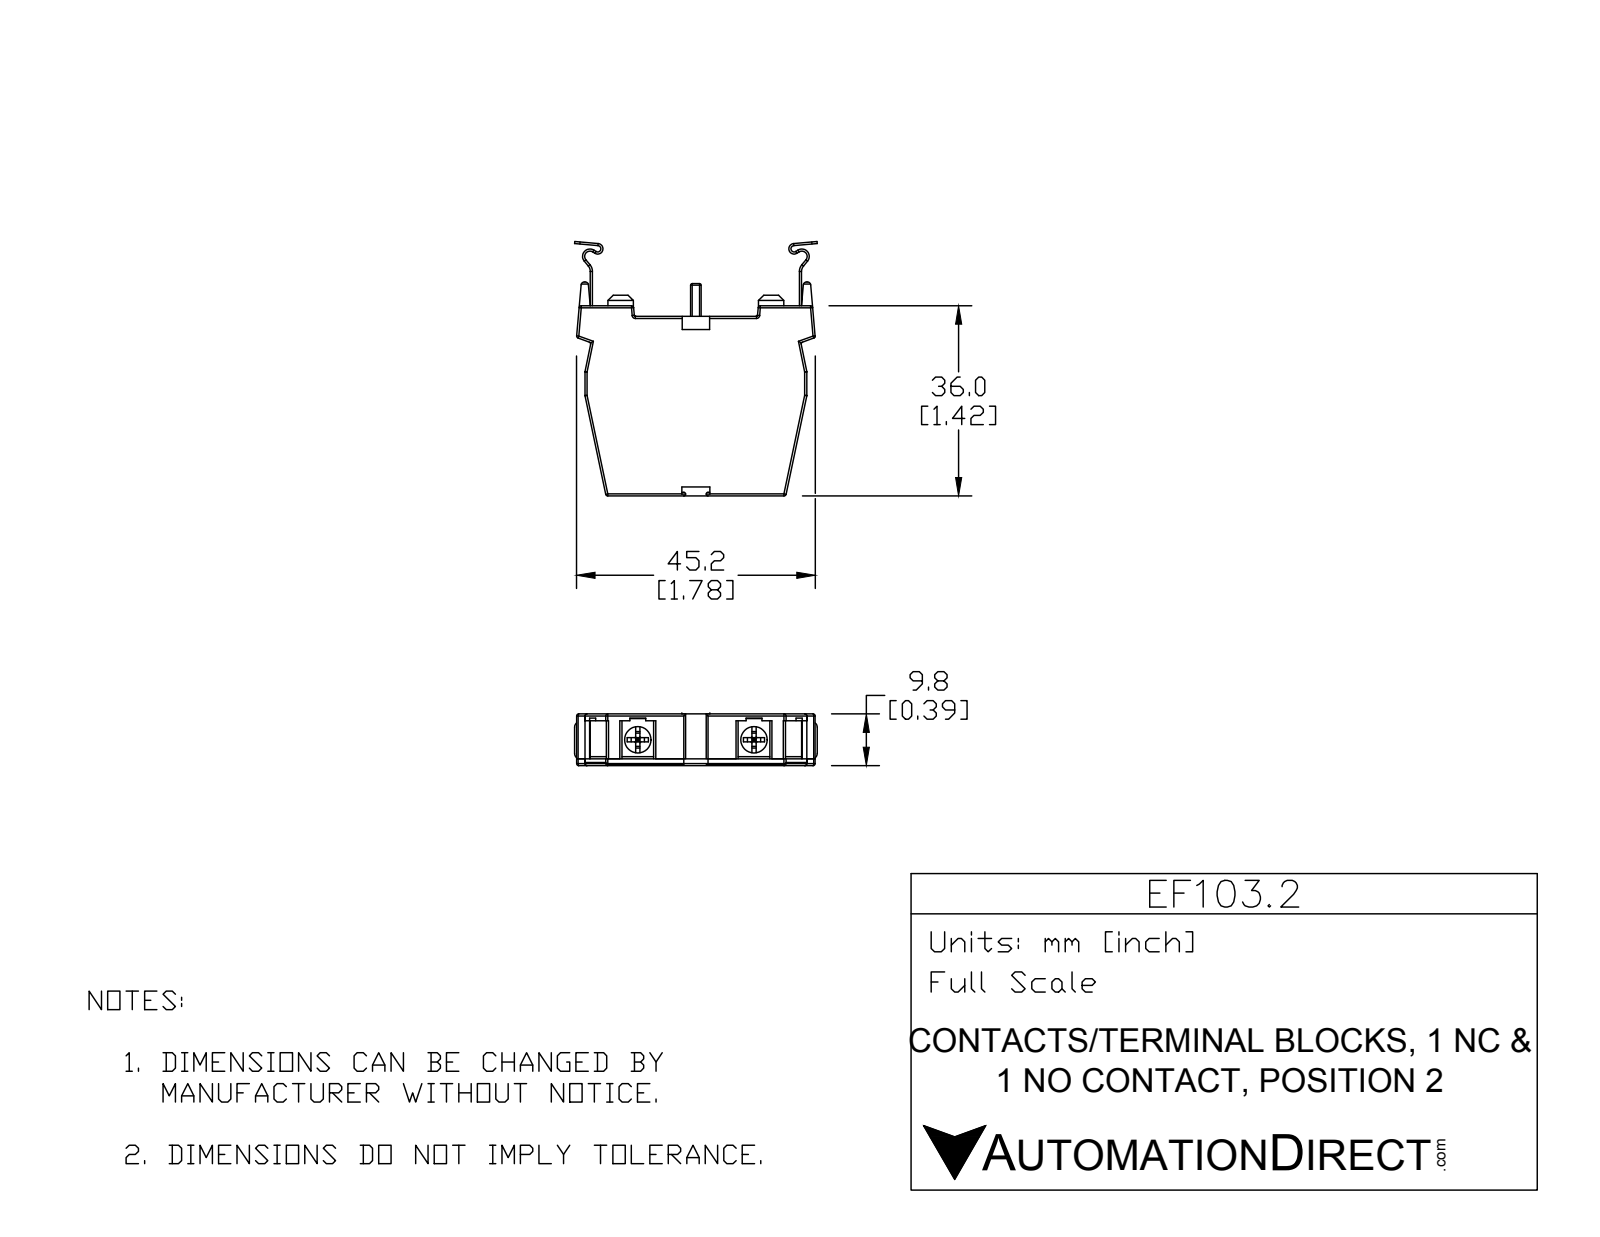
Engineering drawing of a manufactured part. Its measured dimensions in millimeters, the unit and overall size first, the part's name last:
Units: millimetres
Overall size (bounding box): 48.16 × 46.28 × 9.8
Round holes (diameter × count): ⌀5 ×4
Round bosses / shafts (diameter × count): ⌀4 ×4, ⌀4.75 ×2
Partial cylindrical surfaces — rounded edges, fillets, slot ends (radius × count): R0.25 ×44, R0.5 ×8, R1 ×6, R0.6 ×4, R0.6 ×2, R1 ×2, R1.4 ×2, R1.6 ×2
Main face-to-face distances: 9.8, 1.4, 8.4, 34, 7, 2, 0.4, 3.18, 37.18, 36
Hole centre spacings: 21.81
Volume: 12 135 mm³ · Surface area: 6 604 mm²
Bodies: 7 solids, 299 faces (173 planar, 104 cylindrical, 22 other)
Part name (STEP PRODUCT): EF103.2
STEP written by: SolidWorks 2015 (AUTOMOTIVE_DESIGN)
